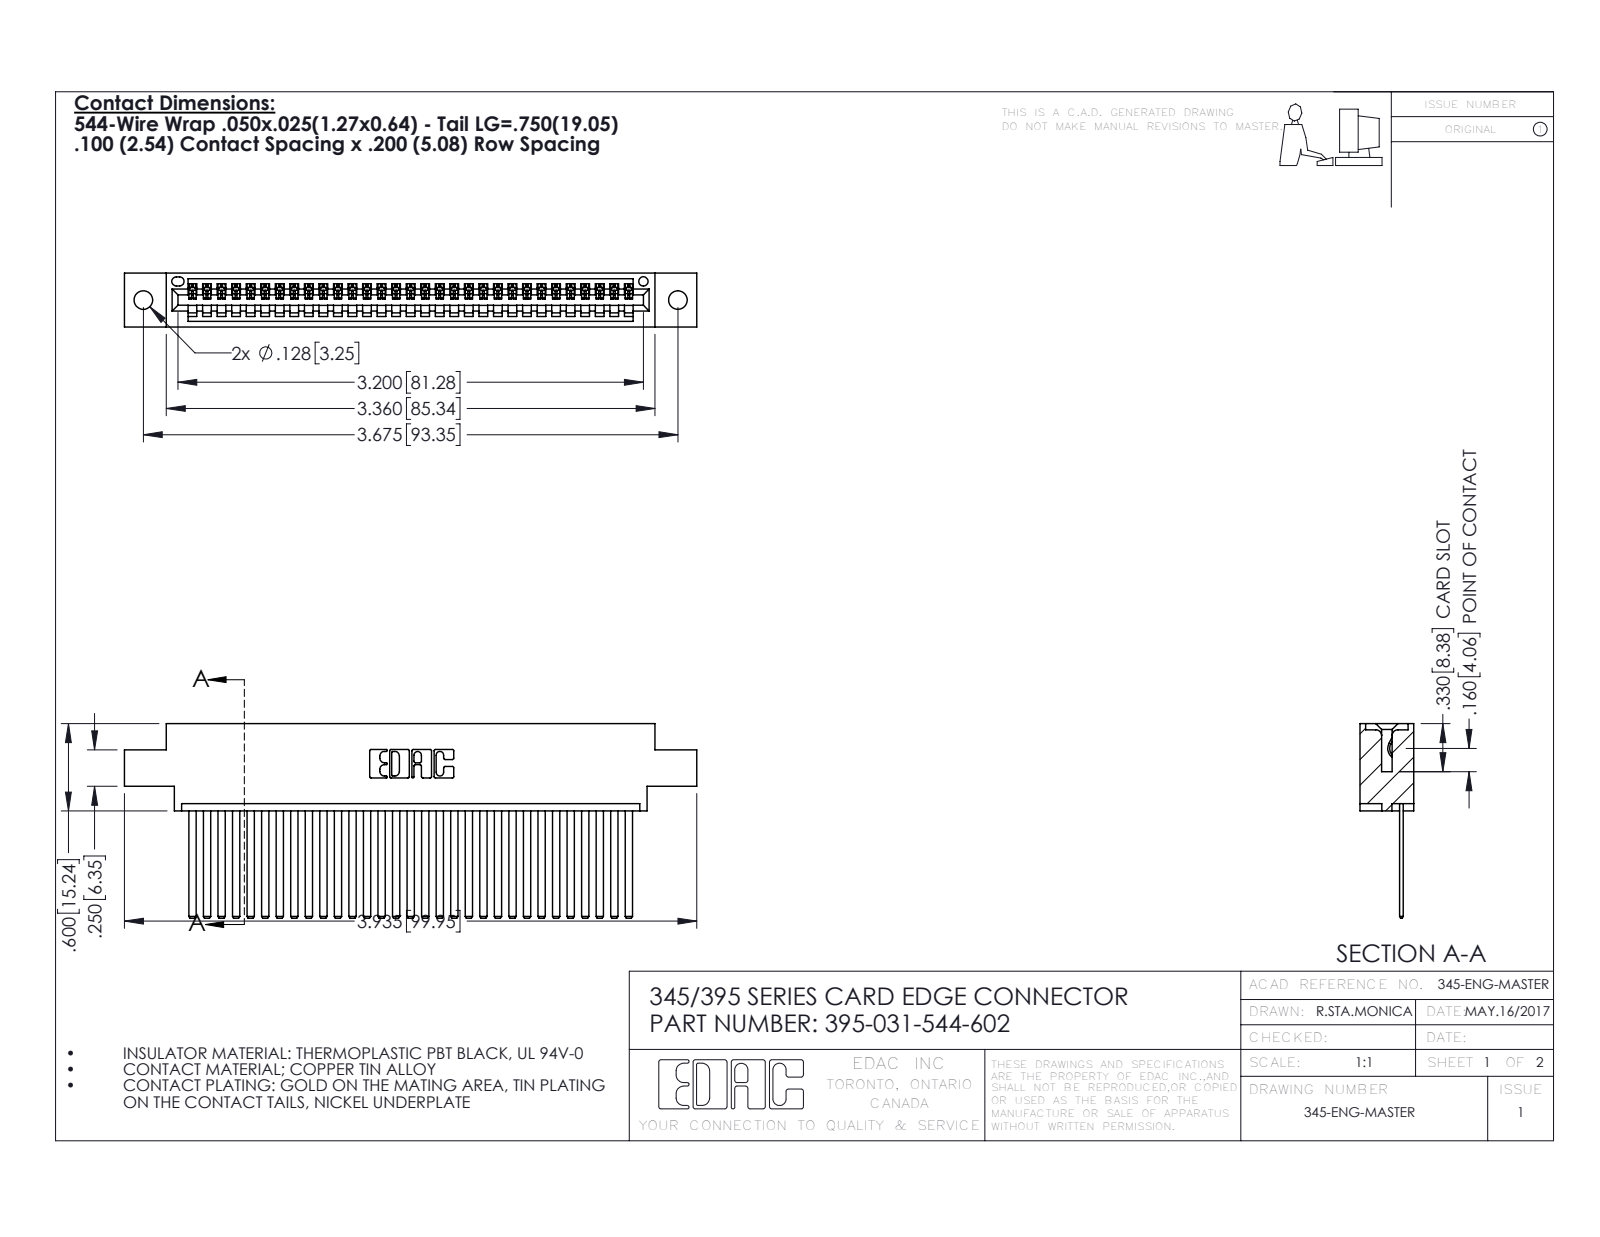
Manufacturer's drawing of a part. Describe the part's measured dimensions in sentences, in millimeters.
The part is named "345-292-001_345-293-144; 395-031-544-602; 345 Part_0.170 Offset - 0.128 Dia". Its 3-D file was written by "SolidWorks 2016 (CONFIG_CONTROL_DESIGN)". It is 32 solids with 1742 faces: 1200 planar, 542 cylindrical and 0 other. Overall it measures 99.9 by 34 by 9.4 millimeters. Its volume is 9 620 cubic millimeters and its surface area 13 550 square millimeters. Round holes: 2 of diameter 3.3, 1 of diameter 1.6. Partial cylindrical surfaces (rounded edges, fillets, slot ends): 62 of radius 0.2, 22 of radius 0.3, 6 of radius 0.2, 6 of radius 0.8, 3 of radius 0.7, 2 of radius 0.8, 2 of radius 1, 1 of radius 0.4. The main face-to-face distances are 1.8, 7.6, 0.6, 2.5, 6.9, 9.4, 5.1, 5.7, 4.4, 3.8. The hole center spacings are 6.9, 87.4, 93.3.
